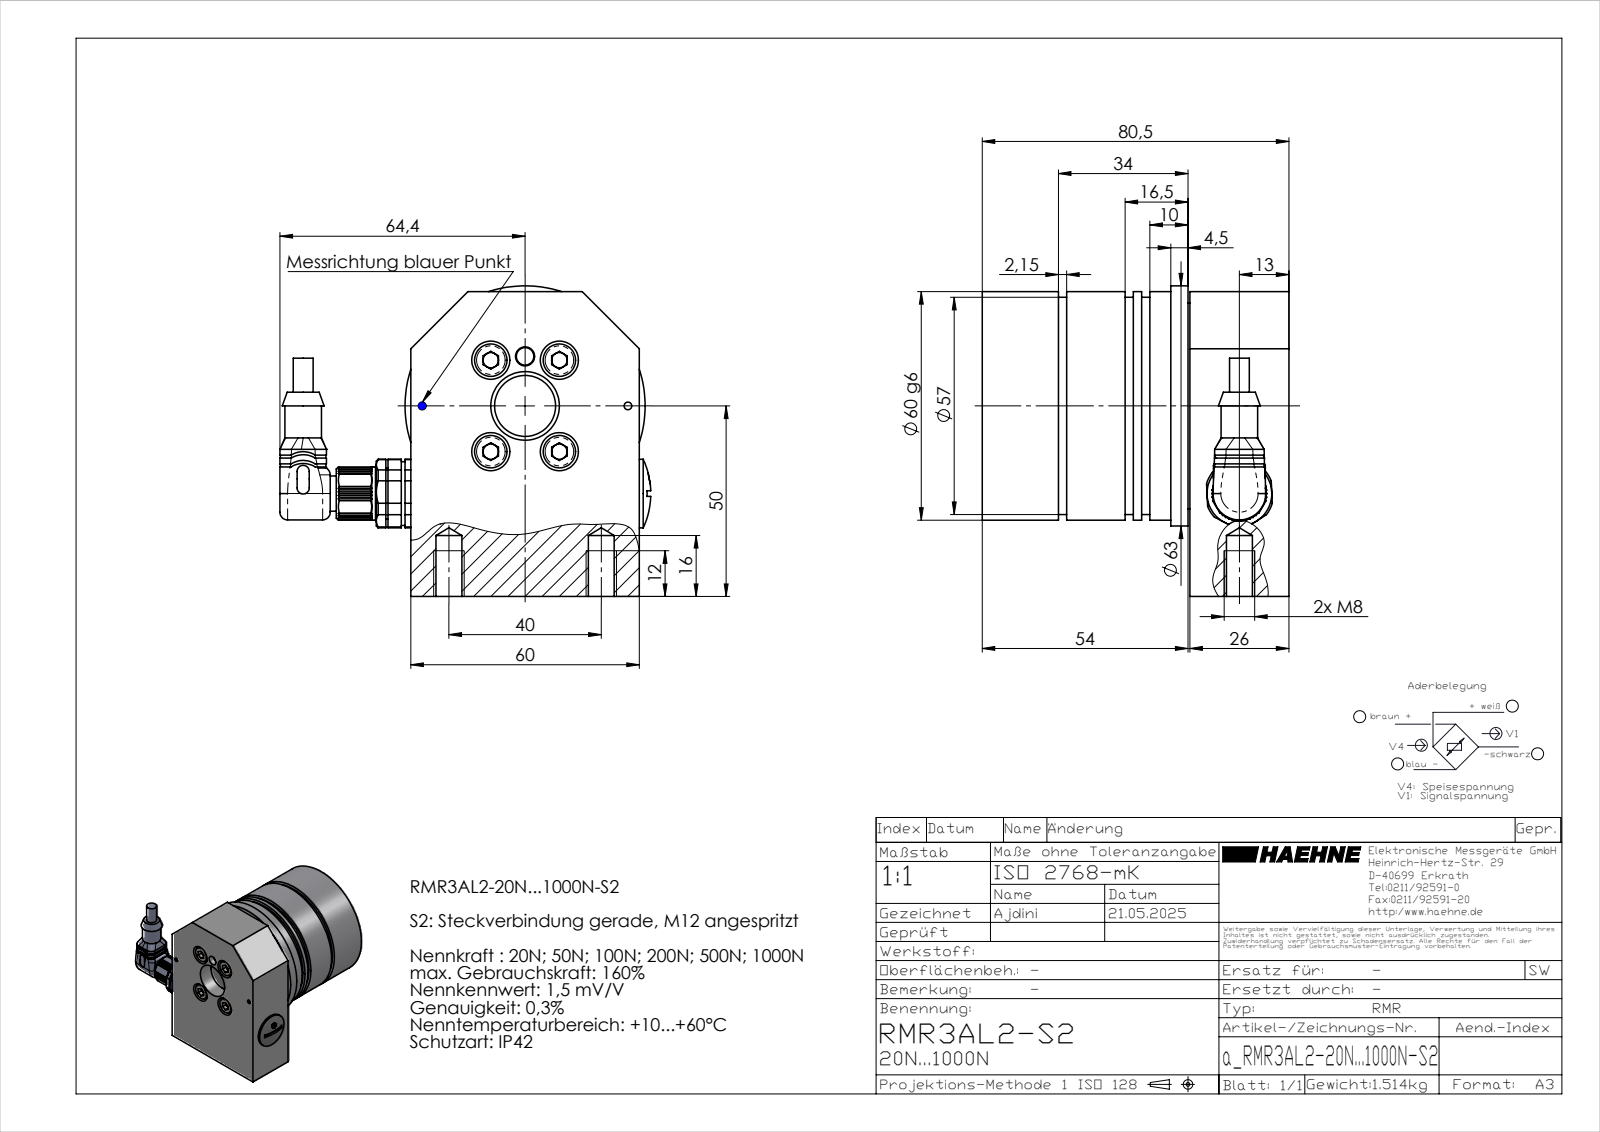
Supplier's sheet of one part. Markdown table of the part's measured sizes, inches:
| quantity | value |
| --- | --- |
| part name | a_RMR3AL2-20N...1000N-S2 |
| STEP written by | SolidWorks 2023 (AUTOMOTIVE_DESIGN) |
| units | inches |
| bodies | 15 solids, 974 faces (533 planar, 248 cylindrical, 193 other) |
| overall size | 3.832 × 3.209 × 3.169 |
| volume | 14.39 in³ |
| surface area | 113.8 in² |
| round holes (diameter × count) | 0.043 × 4, 0.045 × 4, 0.063 × 4, 0.073 × 4, 0.165 × 4, 0.209 × 4, 0.394 × 4, 0.079 × 2, 0.268 × 2, 0.025 × 1, 0.047 × 1, 0.118 × 1 |
| round bosses / shafts (diameter × count) | 0.034 × 5, 0.335 × 4, 0.197 × 4, 0.071 × 4, 0.061 × 4, 0.059 × 4, 0.039 × 4, 2.48 × 1 |
| partial cylindrical surfaces (radius × count) | 0.008 × 16, 0.012 × 9, 0.016 × 4, 0.021 × 4, 0.039 × 4, 0.05 × 4, 0.236 × 4, 0.063 × 2 |
| main face-to-face distances | 0.453, 1.909, 1.457, 2.874, 2.146, 2.441, 0.433, 1.85, 0.591, 1.024 |
| hole center spacings | 0.098, 0.139, 0.591, 0.852, 1.494, 0.197, 0.357, 0.709 |
